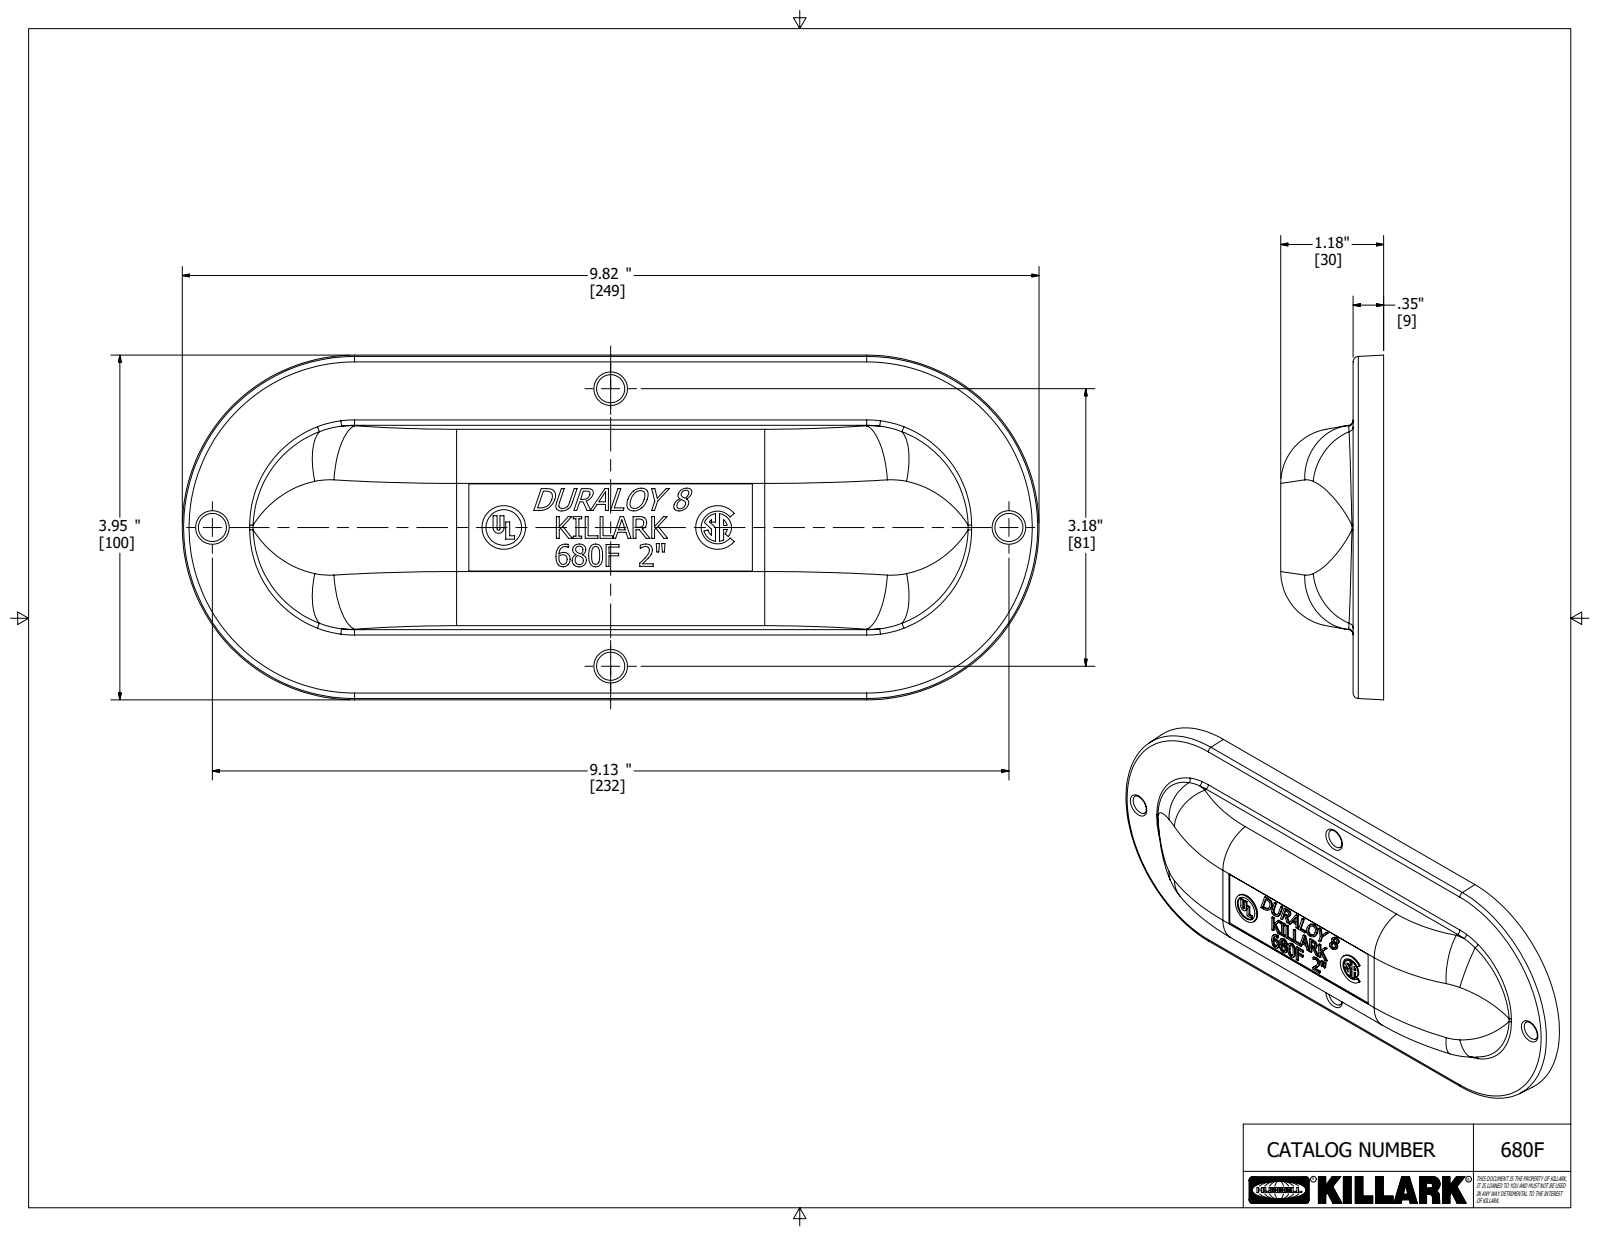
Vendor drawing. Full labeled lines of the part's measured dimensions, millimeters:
Part name (STEP PRODUCT): 21765
STEP written by: Autodesk Inventor 2018 (AUTOMOTIVE_DESIGN)
Units: millimetres
Bodies: 1 solid, 518 faces (236 planar, 38 cylindrical, 244 other)
Overall size (bounding box): 249.4 × 100.3 × 30
Volume: 159 400 mm³ · Surface area: 62 250 mm²
Round holes (diameter × count): ⌀10.3 ×1
Round bosses / shafts (diameter × count): ⌀12.7 ×1
Partial cylindrical surfaces — rounded edges, fillets, slot ends (radius × count): R1.6 ×8, R0.8 ×2, R6.1 ×2, R11.2 ×2, R16 ×2, R90.2 ×2, R95 ×2, R0.4 ×1
Main face-to-face distances: 8.9, 25.1, 16.3, 4.8, 29.5, 20.6, 4.3, 4.7, 4.1, 20.4
